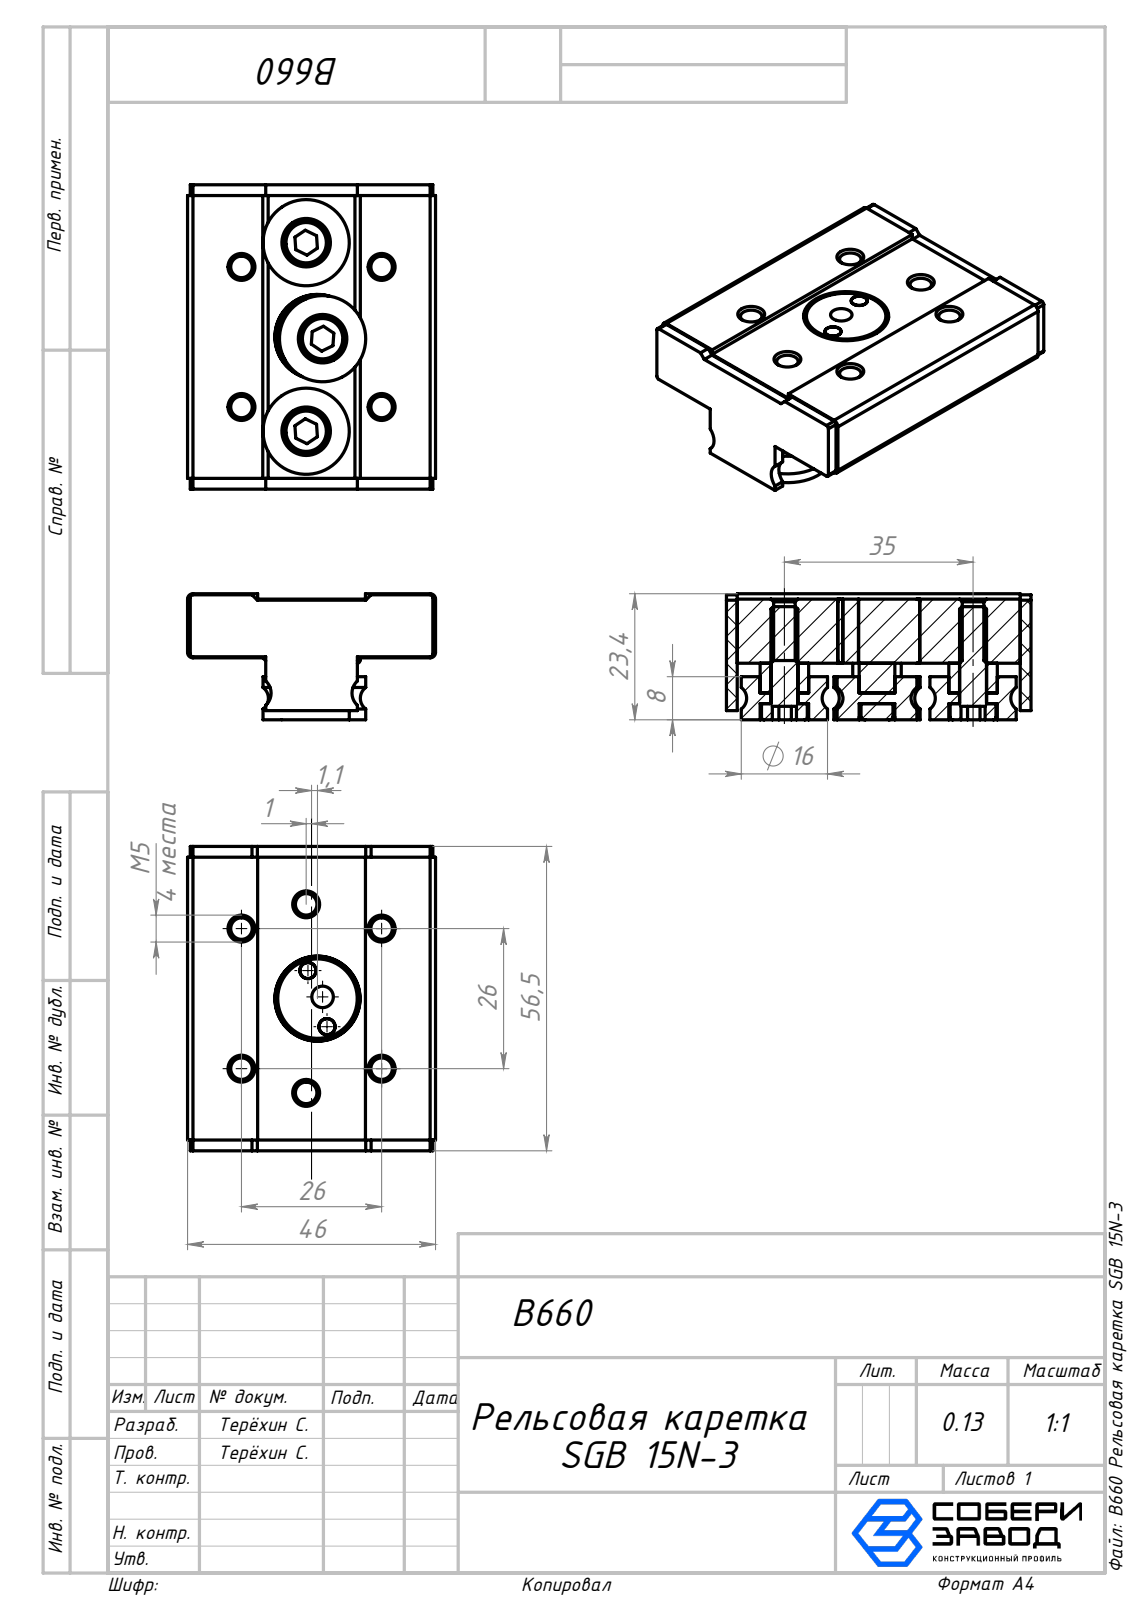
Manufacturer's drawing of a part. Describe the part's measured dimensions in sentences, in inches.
The part is named "B672 Винт_00; B672 Дистанционная втулка_00; Сборка3^B660 Рельсовая каретка SGB 15N-3_00; B660 Деталь для настройки смещения оси_00 (+4 more)". Its 3-D file was written by "SolidWorks 2025 (AUTOMOTIVE_DESIGN)". It is 15 solids with 256 faces: 100 planar, 98 cylindrical and 58 other. Overall it measures 2.224 by 1.811 by 0.921 inches. Its volume is 2.163 cubic inches and its surface area 28.29 square inches. Round holes: 7 of diameter 0.157, 3 of diameter 0.197, 3 of diameter 0.354, 2 of diameter 0.118, 1 of diameter 0.622. Round bosses or shafts: 3 of diameter 0.63, 3 of diameter 0.335, 1 of diameter 0.62. Partial cylindrical surfaces (rounded edges, fillets, slot ends): 4 of radius 0.02, 4 of radius 0.039, 2 of radius 0.119. The main face-to-face distances are 0.469, 0.039, 0.079, 2.146, 2.067, 0.429, 0.508, 2.224, 0.413, 0.453. The hole center spacings are 1.024, 0.217, 0.505, 0.579, 0.694, 0.694, 0.755, 1.291.
